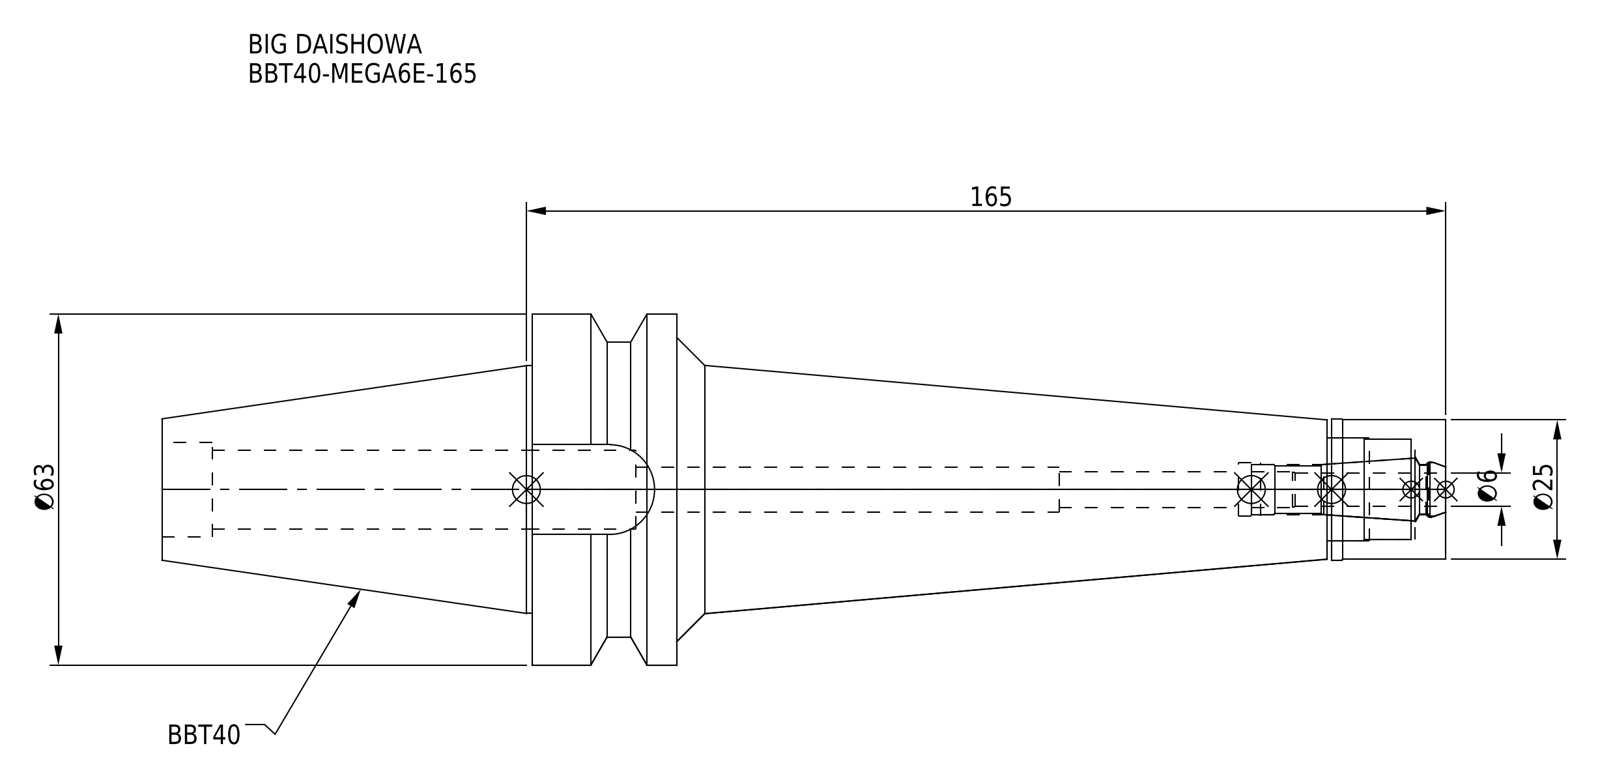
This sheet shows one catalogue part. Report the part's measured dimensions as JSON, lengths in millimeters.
{"part_name": "BBT40ME06165-060_ASM.stp; BBT40-MEGA6E-165; BBT40-MEGA6E-165-060-FreeParts; MEN6_1.stp (+3 more)", "step_written_by": "SolidWorks 2019 (CONFIG_CONTROL_DESIGN)", "units": "millimeters", "bodies": {"solids": 2, "faces": 81, "planar": 21, "cylindrical": 40, "other": 20}, "overall_size": [230.4, 63, 63], "volume_mm3": 242643, "surface_area_mm2": 41973, "round_holes": [[6.4, 1], [8, 1], [9, 1], [9.6, 1], [9.9, 1], [14.2, 1], [17, 1], [18, 1], [18.5, 1]], "round_bosses_or_shafts": [[63, 1], [53, 1], [44.45, 1], [25.3, 1], [25, 1]], "partial_cylinders_radius": [[8.05, 1]], "face_to_face_distances": [26, 138, 164, 45, 230.4, 92.4, 66.4, 20.5, 117.5, 143.5]}
